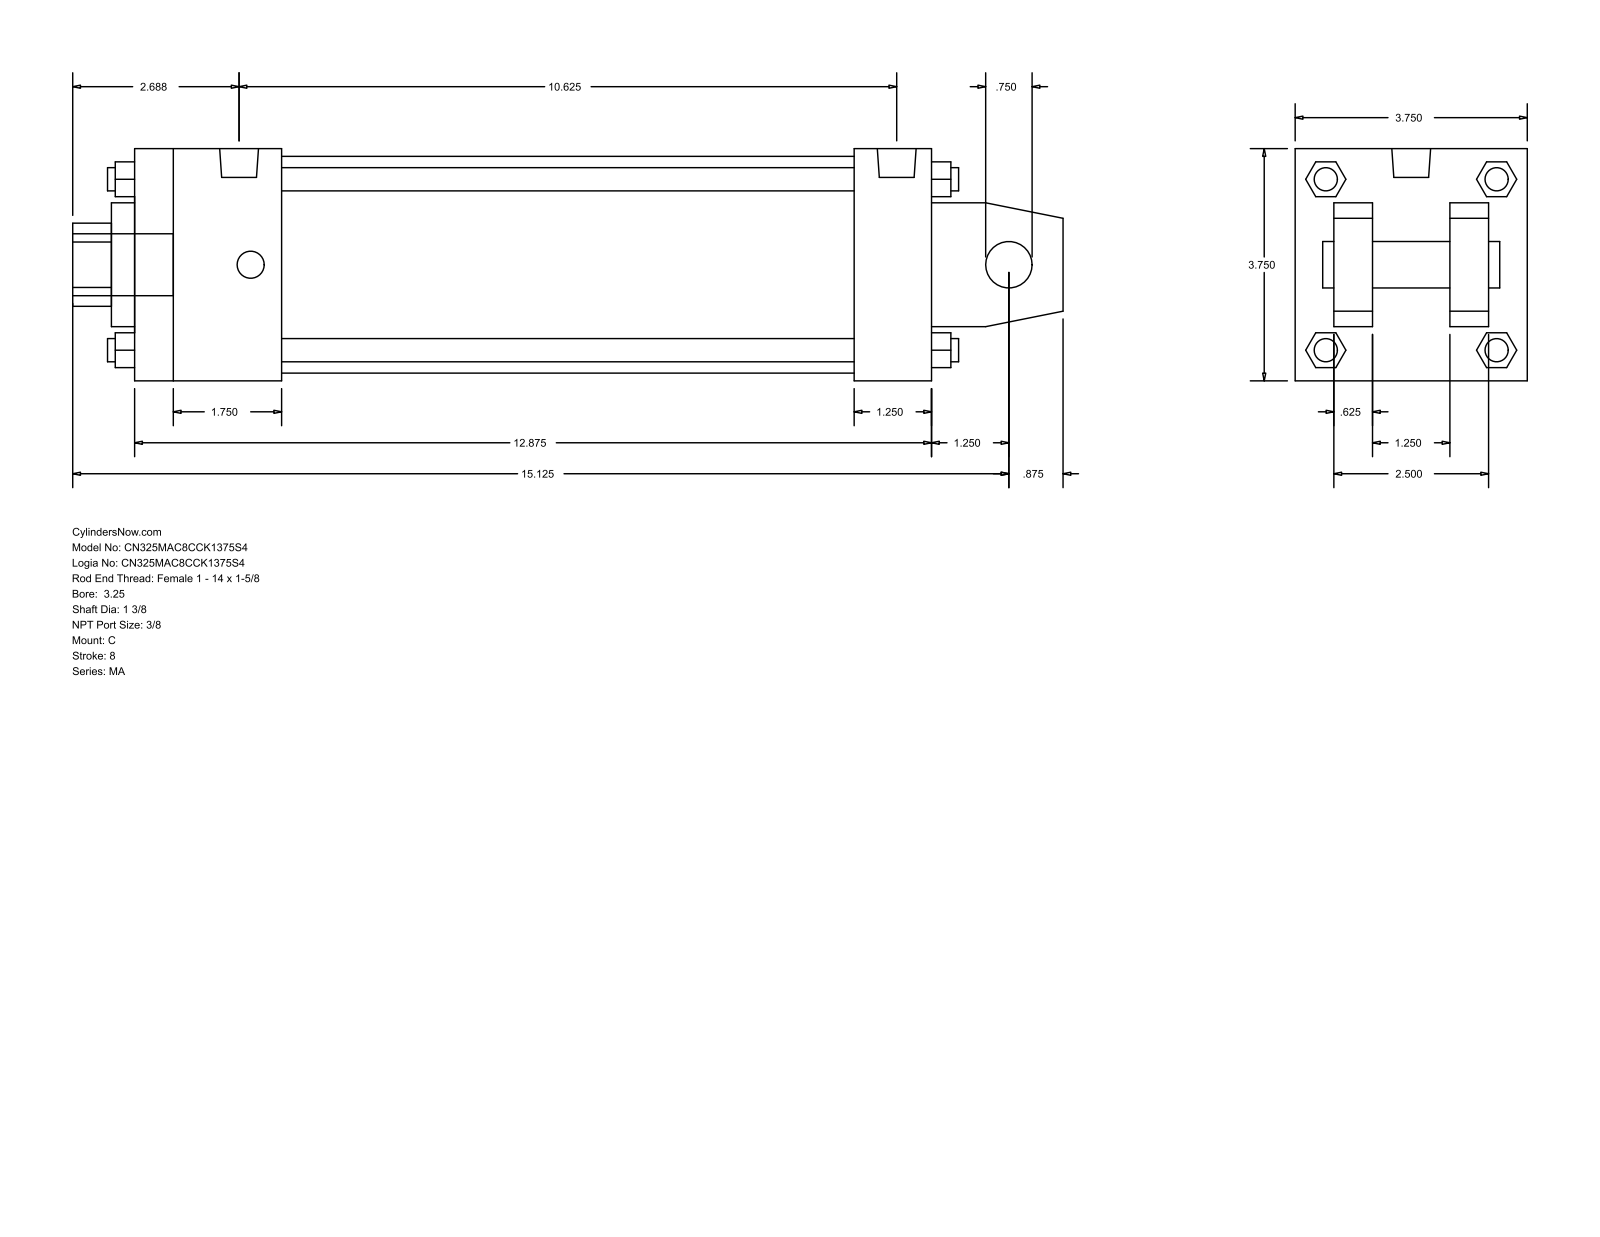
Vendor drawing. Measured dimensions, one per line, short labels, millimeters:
name: MA_C__0325_1.375
written by: GSSL Pune (CONFIG_CONTROL_DESIGN)
unit: mm
bodies: 0 solids, 139 faces (108 planar, 31 cylindrical, 0 other)
size: 406.4 × 95.25 × 95.25
holes: 1× ⌀19.05, 1× ⌀34.92, 1× ⌀50.8, 1× ⌀88.9
bosses: 4× ⌀11.11, 4× ⌀9.53, 2× ⌀15.93, 1× ⌀25.4
rounds: 1× R17.06
face distances: 95.24, 15.87, 63.5, 327.03, 31.74, 79.37, 47.63, 295.28, 31.75, 60.32
